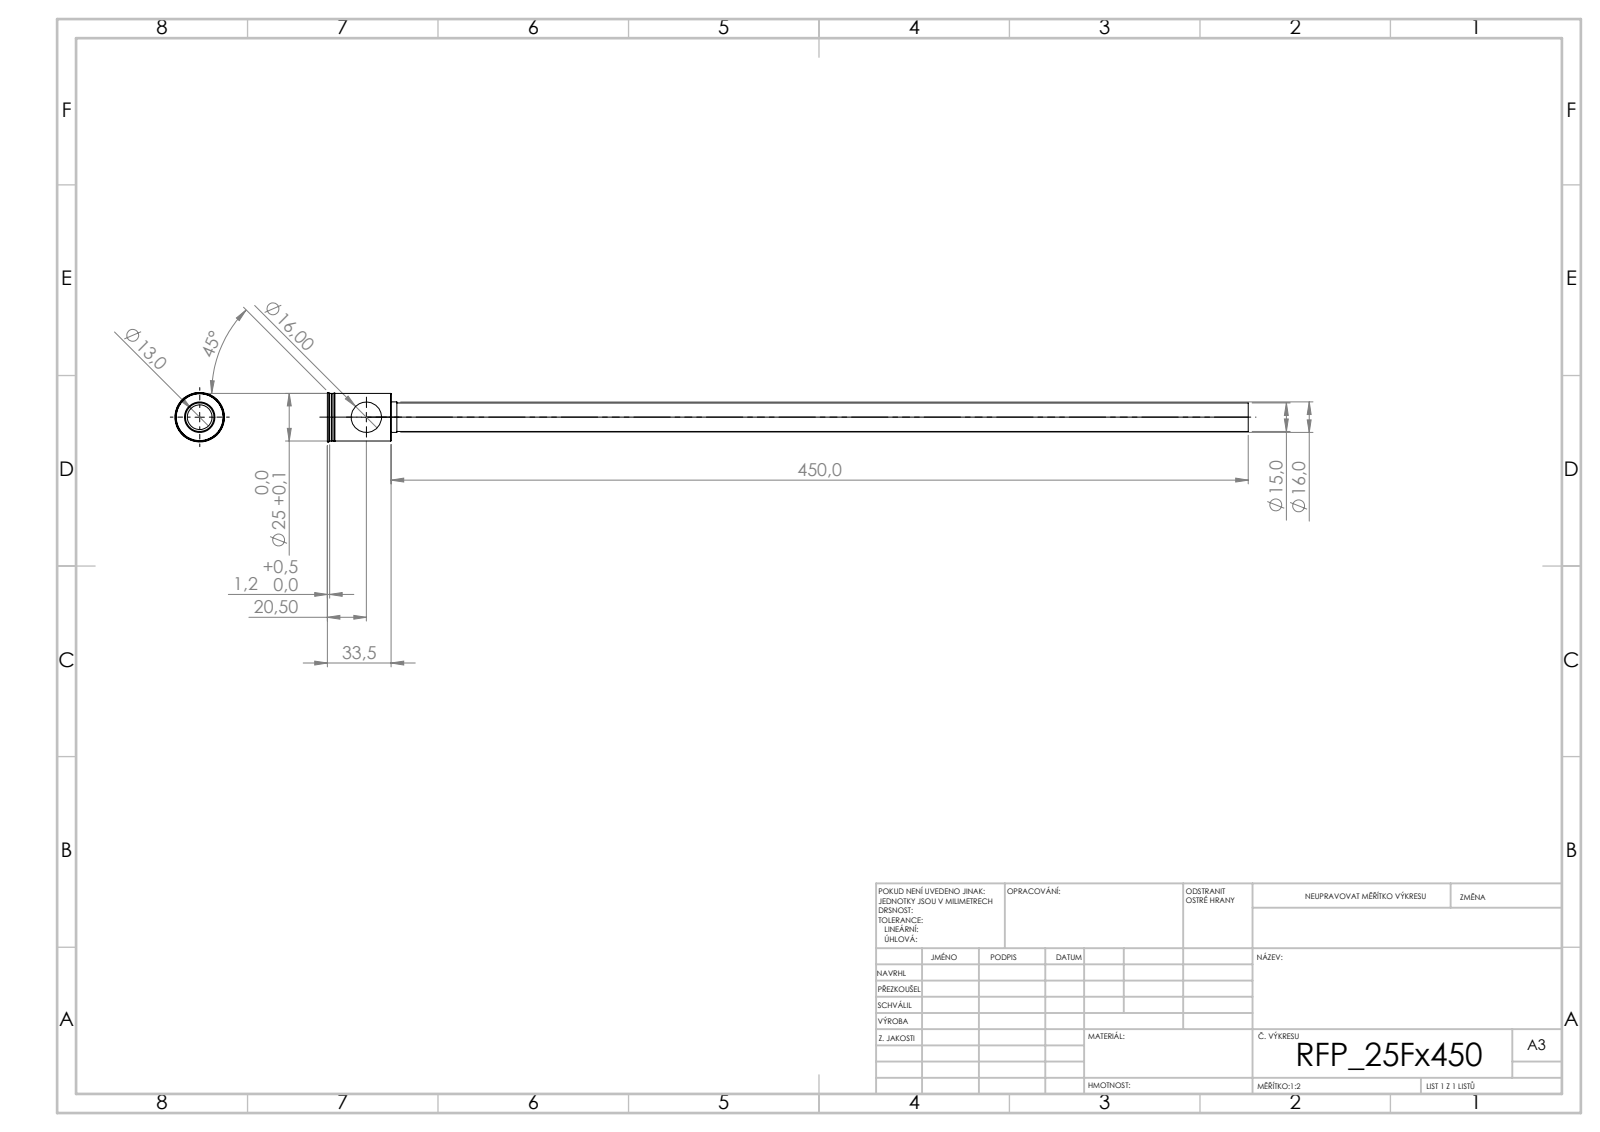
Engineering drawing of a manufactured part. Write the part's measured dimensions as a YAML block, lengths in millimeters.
step_written_by: "SolidWorks 2019 (CONFIG_CONTROL_DESIGN)"
units: millimeters
bodies: {solids: 1, faces: 44, planar: 20, cylindrical: 16, other: 8}
overall_size: [483.5, 26, 26]
volume: 30115
surface_area: 44130
round_holes:
  - {diameter: 13, count: 1}
  - {diameter: 16, count: 1}
round_bosses_or_shafts:
  - {diameter: 26, count: 1}
  - {diameter: 25, count: 1}
  - {diameter: 16, count: 1}
  - {diameter: 15, count: 1}
face_to_face_distances: [31.5, 2, 33.5, 20.4, 450, 481.5, 483.5, 0.5, 447, 3]
